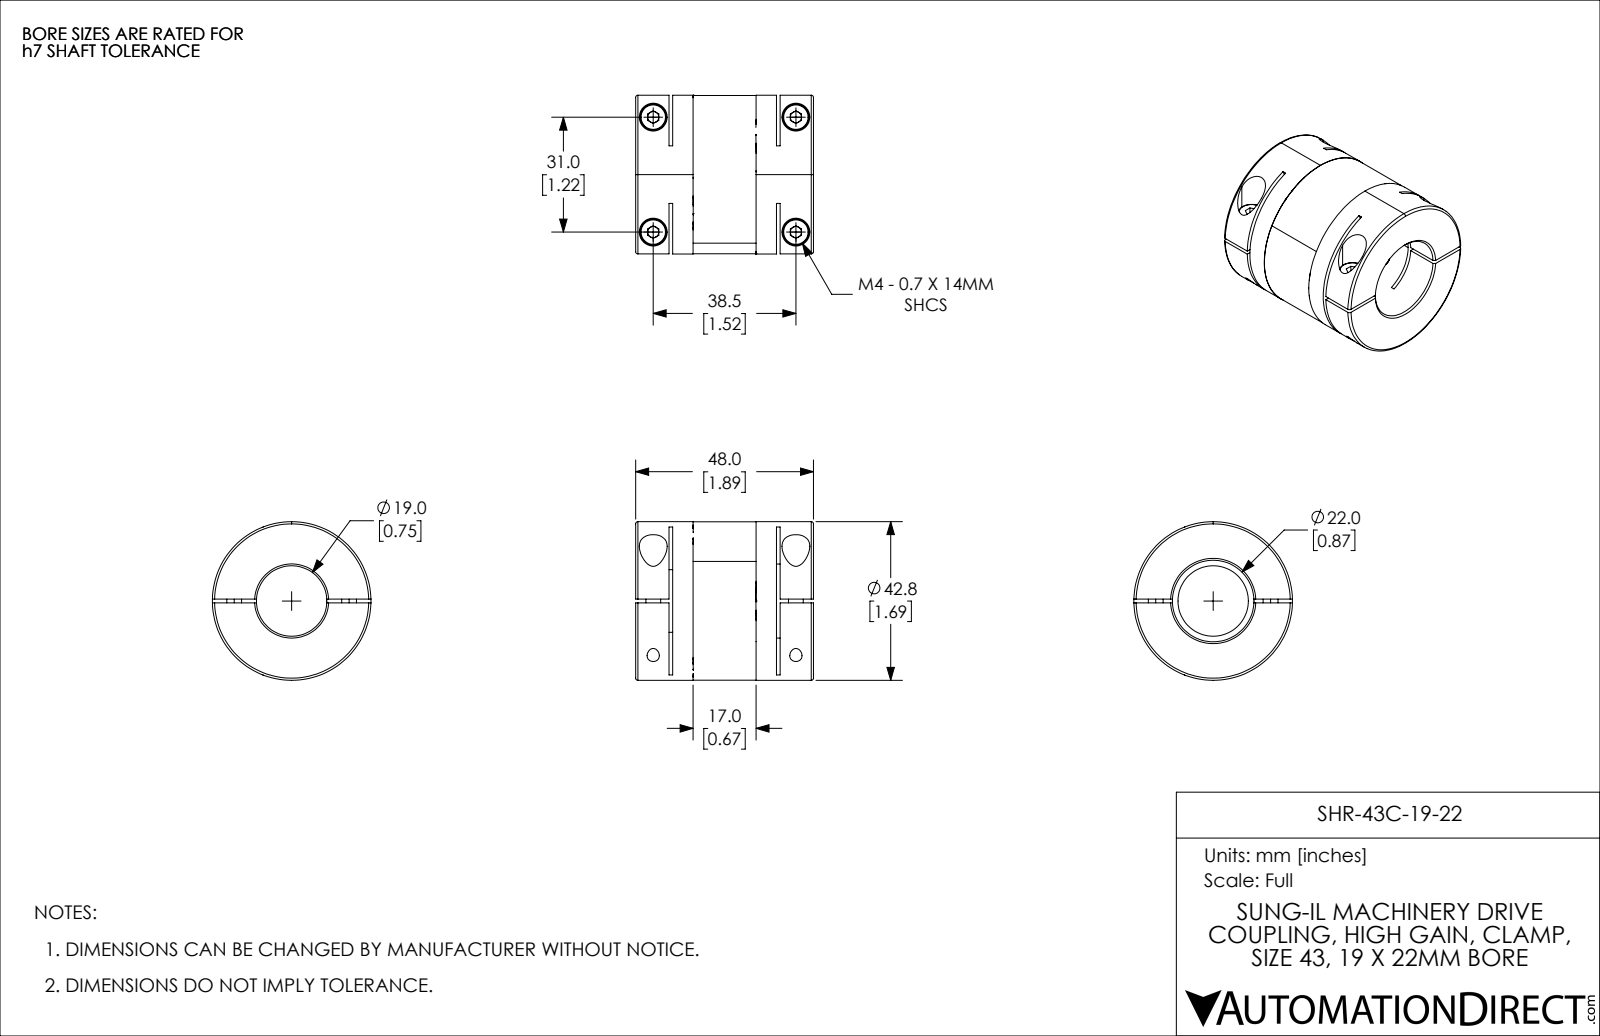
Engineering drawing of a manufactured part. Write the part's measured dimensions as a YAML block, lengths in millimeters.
part_name: "SHR-43C-19-22"
step_written_by: "SolidWorks 2021 (CONFIG_CONTROL_DESIGN)"
units: millimeters
bodies: {solids: 7, faces: 474, planar: 134, cylindrical: 180, other: 160}
overall_size: [48, 42.8, 42.8]
volume: 48119
surface_area: 27291
round_holes:
  - {diameter: 3, count: 4}
  - {diameter: 3.3, count: 4}
  - {diameter: 4.5, count: 4}
  - {diameter: 7.5, count: 4}
  - {diameter: 19, count: 1}
  - {diameter: 22, count: 1}
round_bosses_or_shafts:
  - {diameter: 7, count: 4}
  - {diameter: 4, count: 4}
  - {diameter: 42.8, count: 1}
  - {diameter: 42.7, count: 1}
partial_cylinders:
  - {radius: 3, count: 12}
  - {radius: 4, count: 12}
  - {radius: 11.6, count: 6}
  - {radius: 50, count: 2}
  - {radius: 17.5, count: 1}
  - {radius: 19.5, count: 1}
face_to_face_distances: [1, 15.5, 32.5, 9, 10, 38, 5.5, 22.5, 39, 6.5]
hole_center_spacings: [31, 38.5, 49.43]
